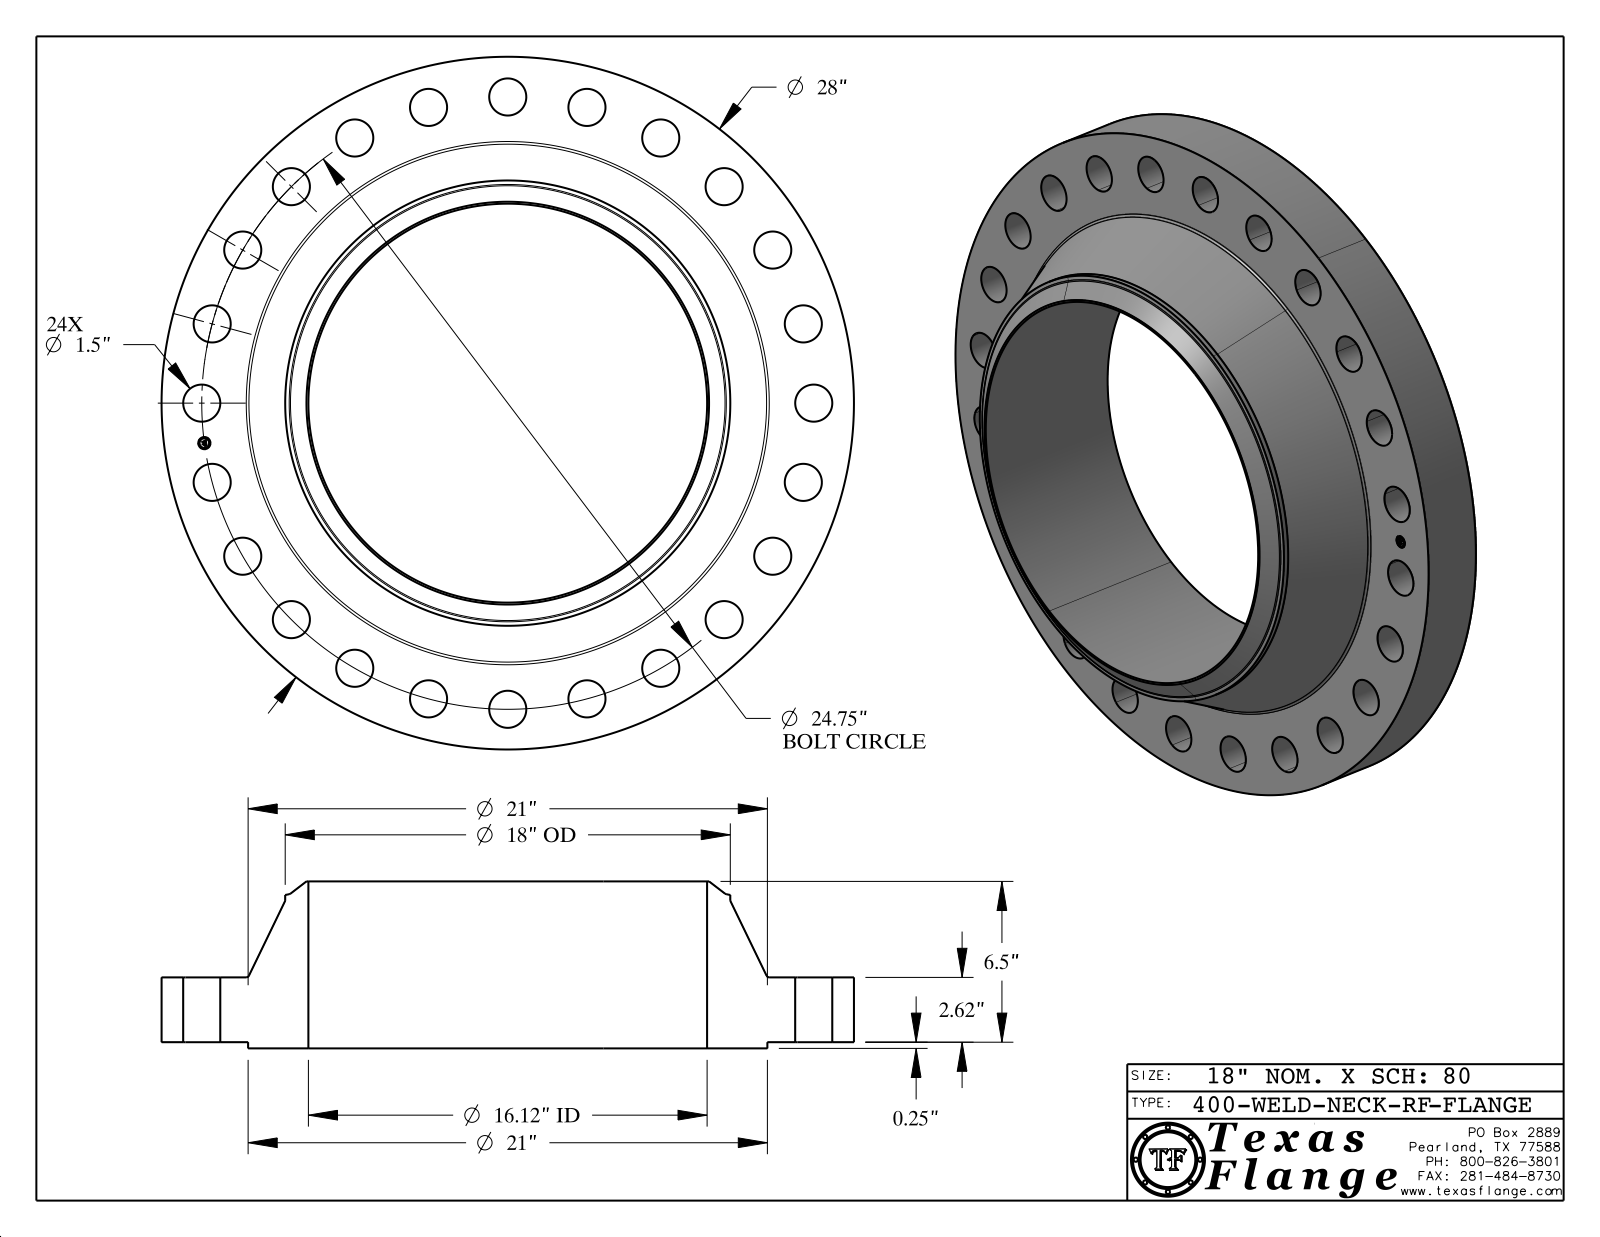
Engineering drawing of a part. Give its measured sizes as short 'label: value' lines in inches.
name: 400-WELD-NECK-RF
written by: CATIA V5 STEP AP214 (AUTOMOTIVE_DESIGN)
unit: in
bodies: 1 solid, 455 faces (369 planar, 76 cylindrical, 10 other)
size: 28 × 28 × 6.75
volume: 1 322 in³; area: 1 764 in²
holes: 24× ⌀1.5, 1× ⌀0.495, 1× ⌀16.124
bosses: 8× ⌀0.03, 1× ⌀28, 1× ⌀21, 1× ⌀18, 1× ⌀0.39
face distances: 2.62, 0.25, 2.87, 6.75, 6.5, 3.88, 2.855, 2.605, 0.015, 3.895
hole spacings: 12.375, 9.471, 15.067, 17.501, 21.434, 22.866, 23.906, 3.23
